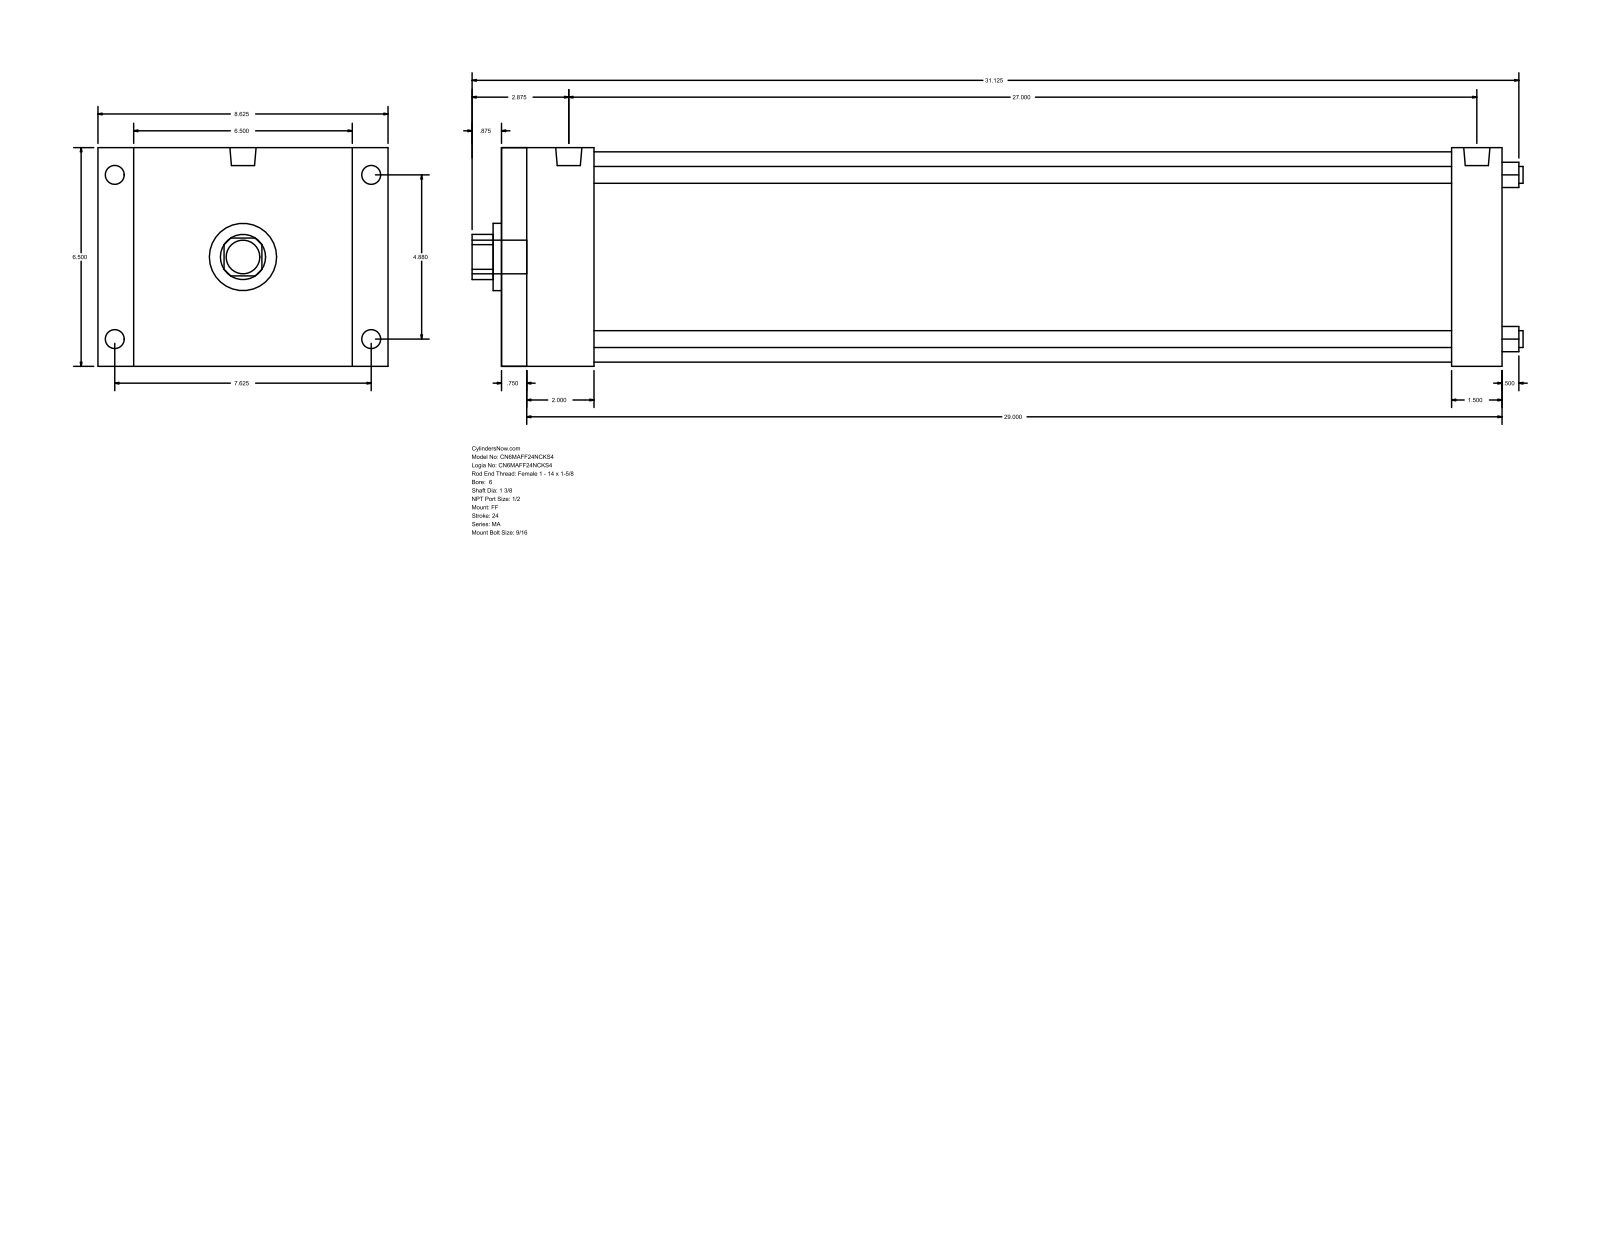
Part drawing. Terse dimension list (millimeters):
name: MA_FF__0600_1.375
written by: GSSL Pune (CONFIG_CONTROL_DESIGN)
unit: mm
bodies: 0 solids, 92 faces (64 planar, 28 cylindrical, 0 other)
size: 793.75 × 219.07 × 165.1
holes: 4× ⌀12.7, 1× ⌀34.92, 1× ⌀50.8, 1× ⌀158.75
bosses: 4× ⌀17.46, 4× ⌀14.29, 2× ⌀19.77, 1× ⌀25.4
rounds: 1× R17.06
face distances: 165.1, 755.65, 15.87, 739.78, 66.67, 50.8, 688.98, 717.54, 701.67, 650.87
hole spacings: 87.65, 123.96, 175.31
